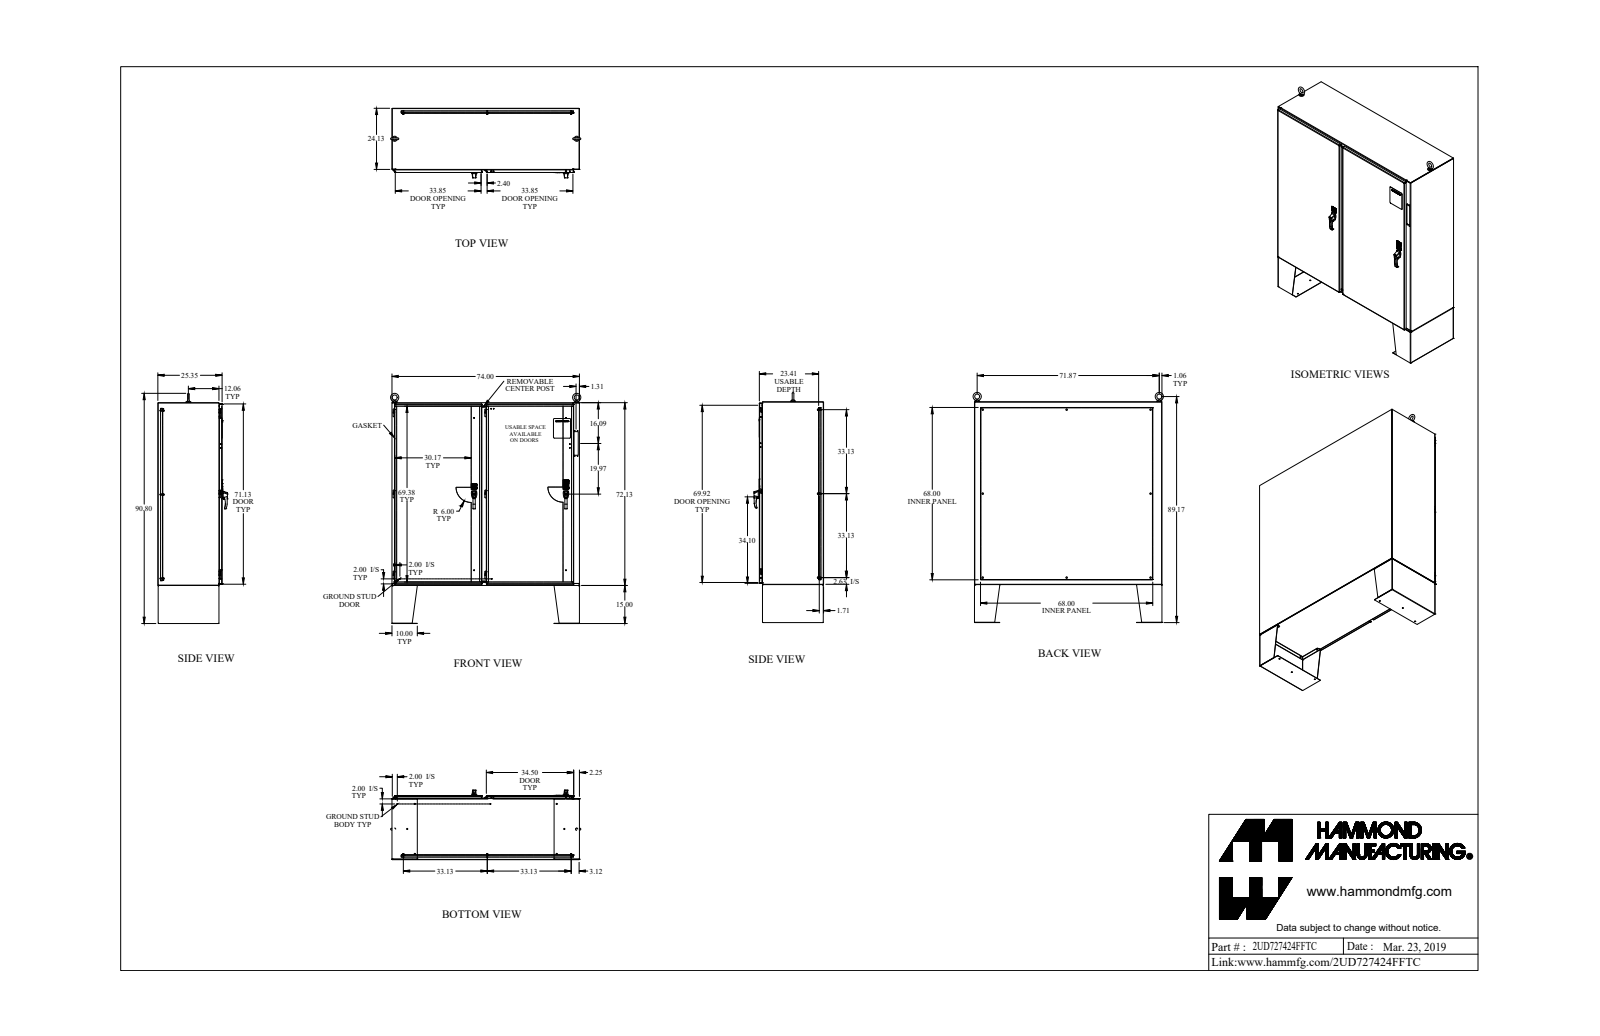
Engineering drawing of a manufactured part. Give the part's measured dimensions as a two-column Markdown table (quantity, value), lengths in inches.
| quantity | value |
| --- | --- |
| part name | 2UD727424FFTC |
| STEP written by | SolidWorks 2018 (AUTOMOTIVE_DESIGN) |
| units | inches |
| bodies | 214 solids, 3138 faces (1822 planar, 930 cylindrical, 386 other) |
| overall size | 90.799 × 75.122 × 27.466 |
| volume | 5 194 in³ |
| surface area | 56 432 in² |
| round holes (diameter × count) | 0.437 × 14, 0.281 × 11, 0.307 × 11, 0.196 × 10, 0.25 × 10, 0.35 × 8, 0.257 × 6, 0.313 × 6, 0.445 × 5, 0.28 × 4, 0.282 × 4, 0.375 × 4 |
| round bosses / shafts (diameter × count) | 0.25 × 19, 1 × 14, 0.65 × 9, 0.375 × 9, 0.33 × 9, 0.281 × 8, 0.75 × 6, 0.53 × 6 |
| partial cylindrical surfaces (radius × count) | 0.125 × 62, 0.06 × 51, 0.5 × 38, 0.017 × 32, 0.185 × 30, 0.03 × 28, 0.048 × 20, 0.143 × 20 |
| main face-to-face distances | 0.125, 0.072, 23.431, 25.368, 25.243, 1.937, 1.812, 1.741, 1.865, 23.503 |
| hole center spacings | 74.07, 36.25, 66.25, 8.126, 10.306, 11.237, 21.457, 33.125 |
